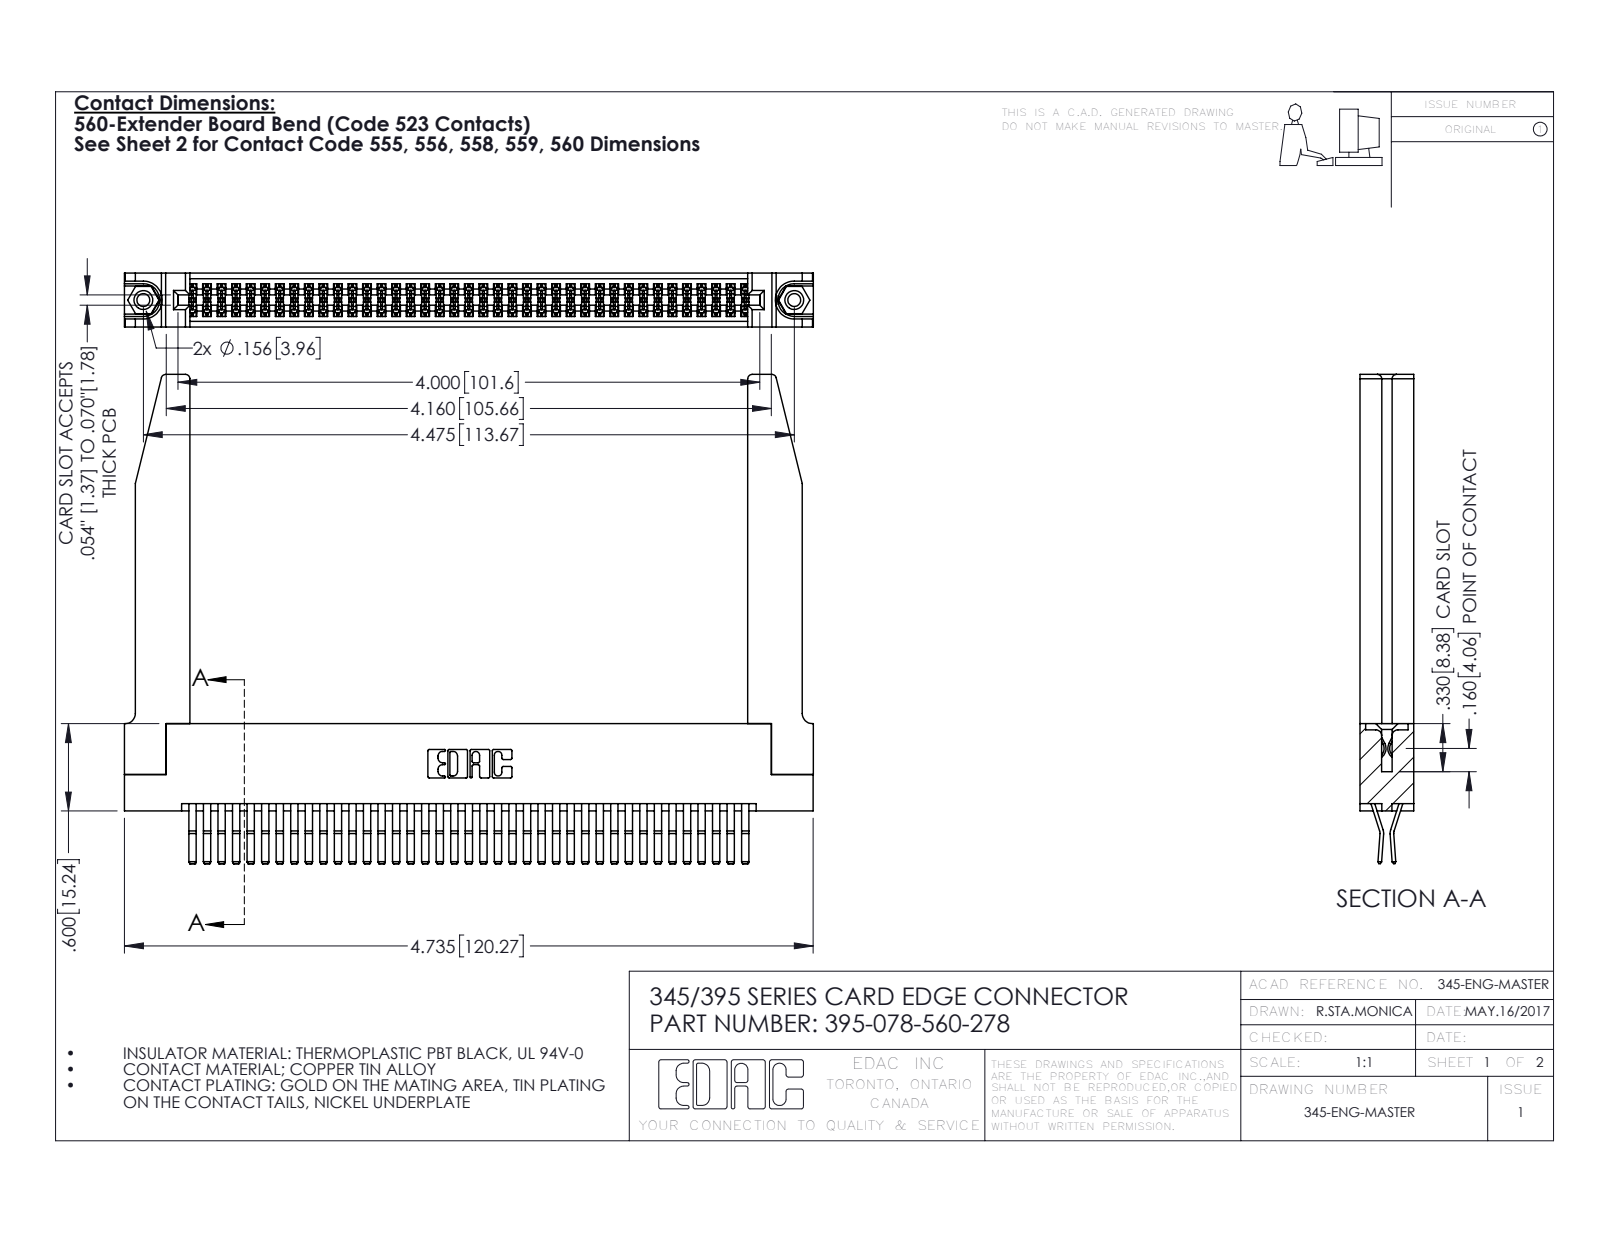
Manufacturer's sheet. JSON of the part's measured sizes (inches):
{"part_name": "345-292-001_560 Tail; 345 Part_Flush Mounting Lugs - 0.156 Dia-TH; 345-220-078_345-220-078; 395-078-560-278 (+1 more)", "step_written_by": "SolidWorks 2016 (CONFIG_CONTROL_DESIGN)", "units": "inches", "bodies": {"solids": 83, "faces": 4416, "planar": 2796, "cylindrical": 1568, "other": 52}, "overall_size": [4.736, 3.362, 0.37], "volume_in3": 1.217, "surface_area_in2": 40.43, "round_holes": [[0.089, 2], [0.125, 2], [0.156, 2], [0.064, 1]], "round_bosses_or_shafts": [[0.155, 2]], "partial_cylinders_radius": [[0.006, 117], [0.01, 22], [0.03, 8], [0.007, 6], [0.031, 6], [0.026, 3], [0.01, 2], [0.014, 2]], "face_to_face_distances": [0.37, 0.072, 0.298, 0.025, 0.2, 0.098, 0.272, 0.225, 0.148, 0.15], "hole_center_spacings": [0.27, 4.239, 4.475]}
